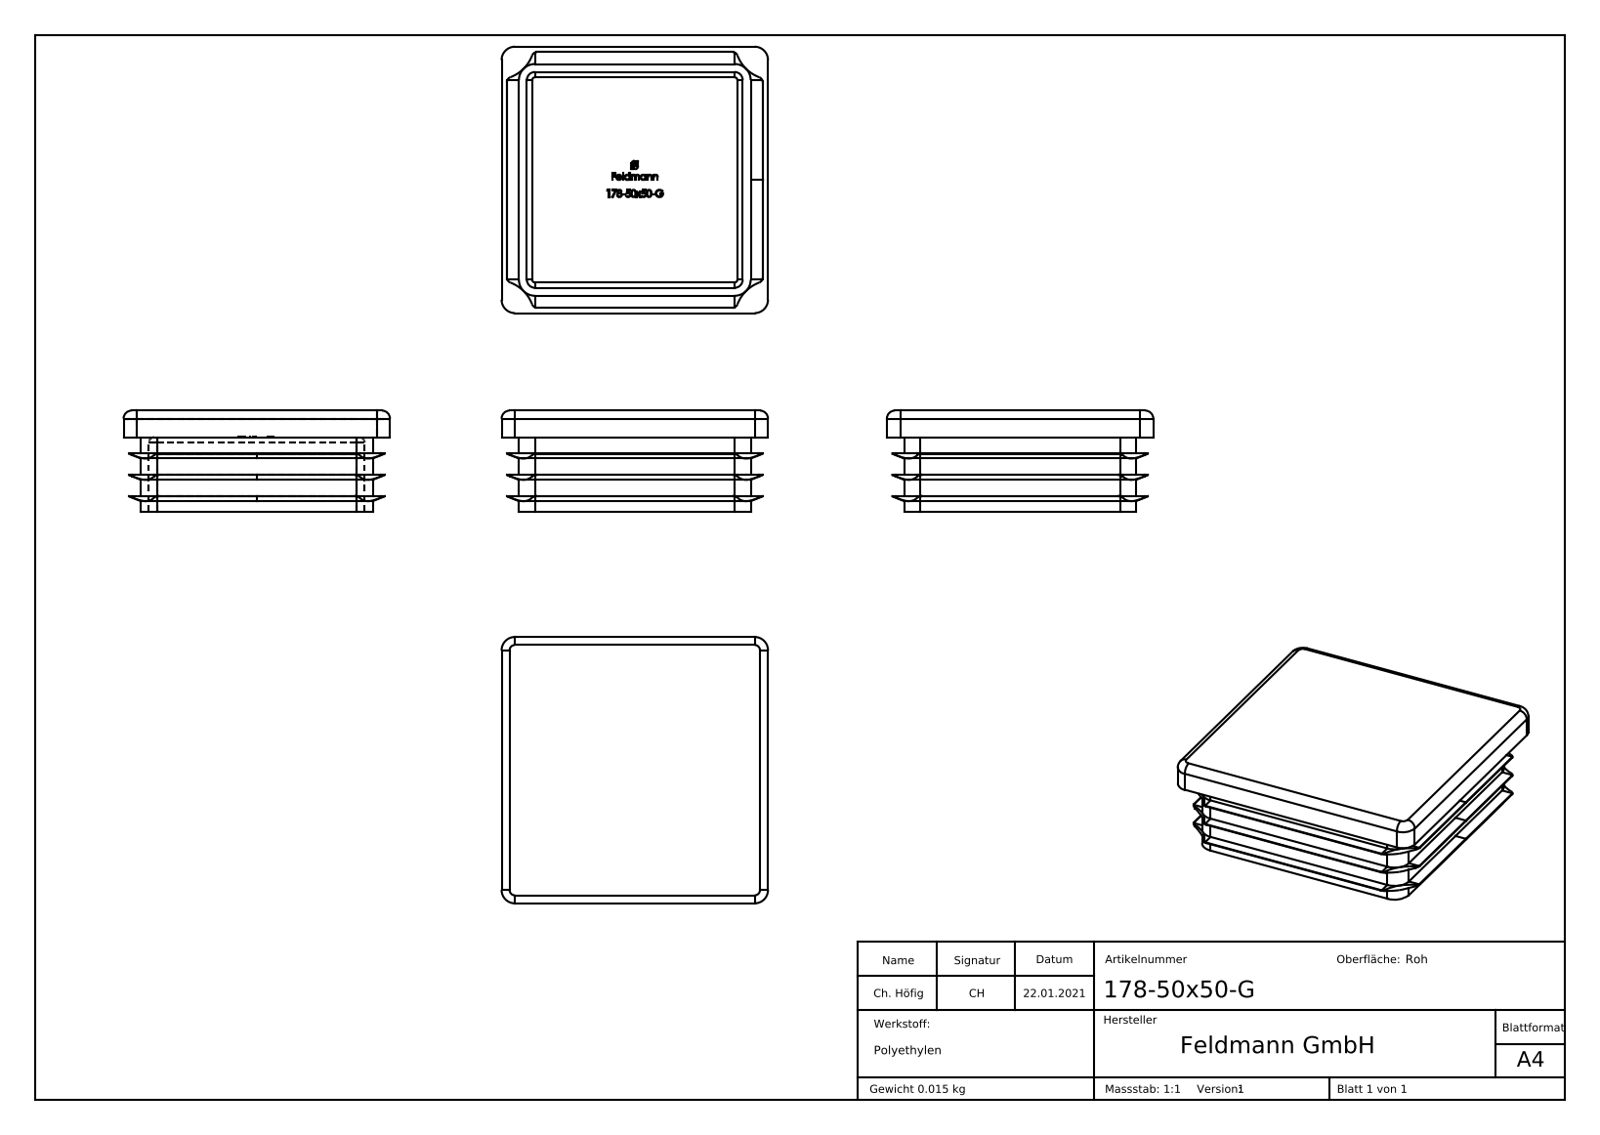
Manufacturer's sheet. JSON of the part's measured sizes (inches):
{"part_name": "178-50X50-G", "step_written_by": "SolidWorks 2018 (CONFIG_CONTROL_DESIGN)", "units": "inches", "bodies": {"solids": 1, "faces": 474, "planar": 231, "cylindrical": 83, "other": 160}, "overall_size": [1.969, 1.969, 0.748], "volume_in3": 1.003, "surface_area_in2": 18.84, "partial_cylinders_radius": [[0.039, 12], [0.059, 8], [0.098, 4], [0.118, 4], [0.276, 4]], "face_to_face_distances": [0.197, 0.059, 1.654, 1.594, 1.713, 0.157, 0.315, 0.128, 0.187, 1.781]}
